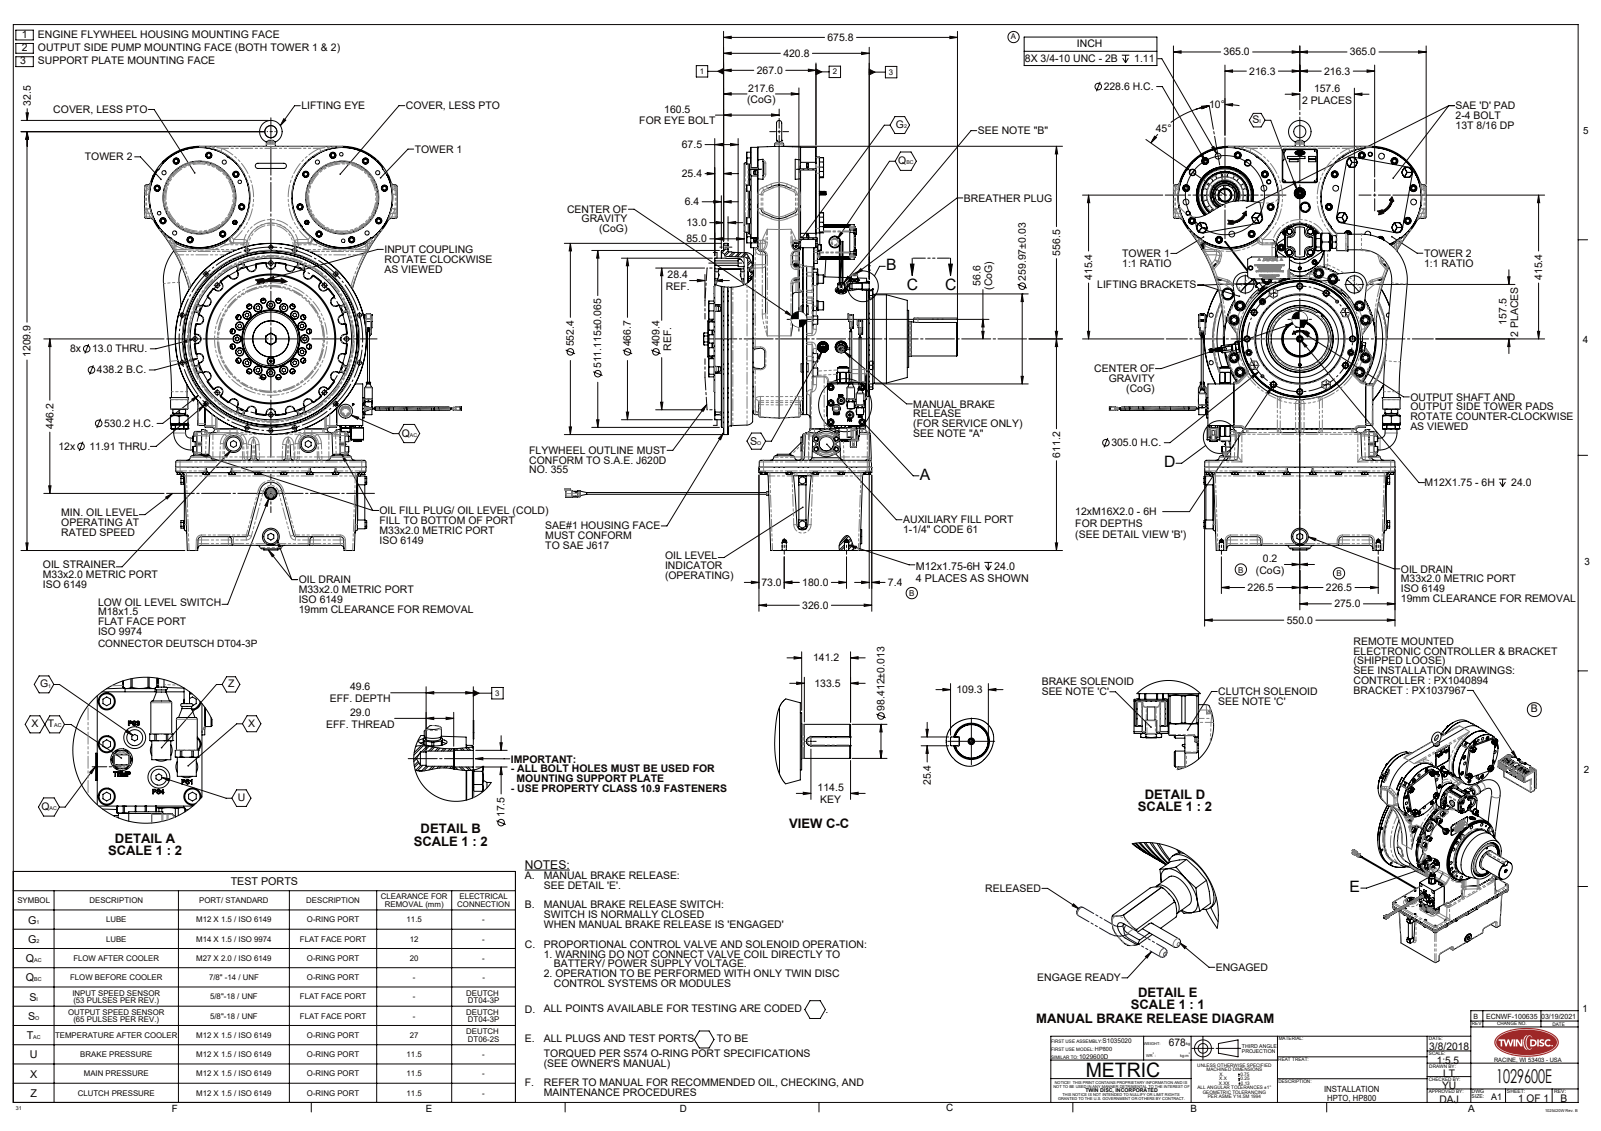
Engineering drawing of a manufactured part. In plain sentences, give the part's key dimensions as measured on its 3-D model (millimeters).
The part is named "1029600E". Its 3-D file was written by "SolidWorks 2019 (AUTOMOTIVE_DESIGN)". It is 0 solids with 3778 faces: 1728 planar, 1065 cylindrical and 985 other. Overall it measures 1242.39 by 1134.48 by 915.08 millimeters. Round holes: 21 of diameter 14, 19 of diameter 8.5, 18 of diameter 24, 16 of diameter 20, 12 of diameter 11.91, 12 of diameter 17.5, 9 of diameter 18, 8 of diameter 12.02, 8 of diameter 13, 8 of diameter 16.67, 5 of diameter 12, 5 of diameter 49. Round bosses or shafts: 18 of diameter 18, 13 of diameter 24, 7 of diameter 28.26, 6 of diameter 40.8, 5 of diameter 16, 4 of diameter 16.66, 4 of diameter 2.79, 3 of diameter 30.15. Partial cylindrical surfaces (rounded edges, fillets, slot ends): 108 of radius 10, 106 of radius 5, 65 of radius 2.54, 28 of radius 12.7, 26 of radius 3, 15 of radius 1, 12 of radius 1.27, 11 of radius 12.5. The main face-to-face distances are 0.6, 20.6, 10.6, 141.12, 130.52, 7, 38, 45, 20, 9.65. The hole center spacings are 75, 225, 375, 150, 309.23, 86.1, 112.5, 140.26.
